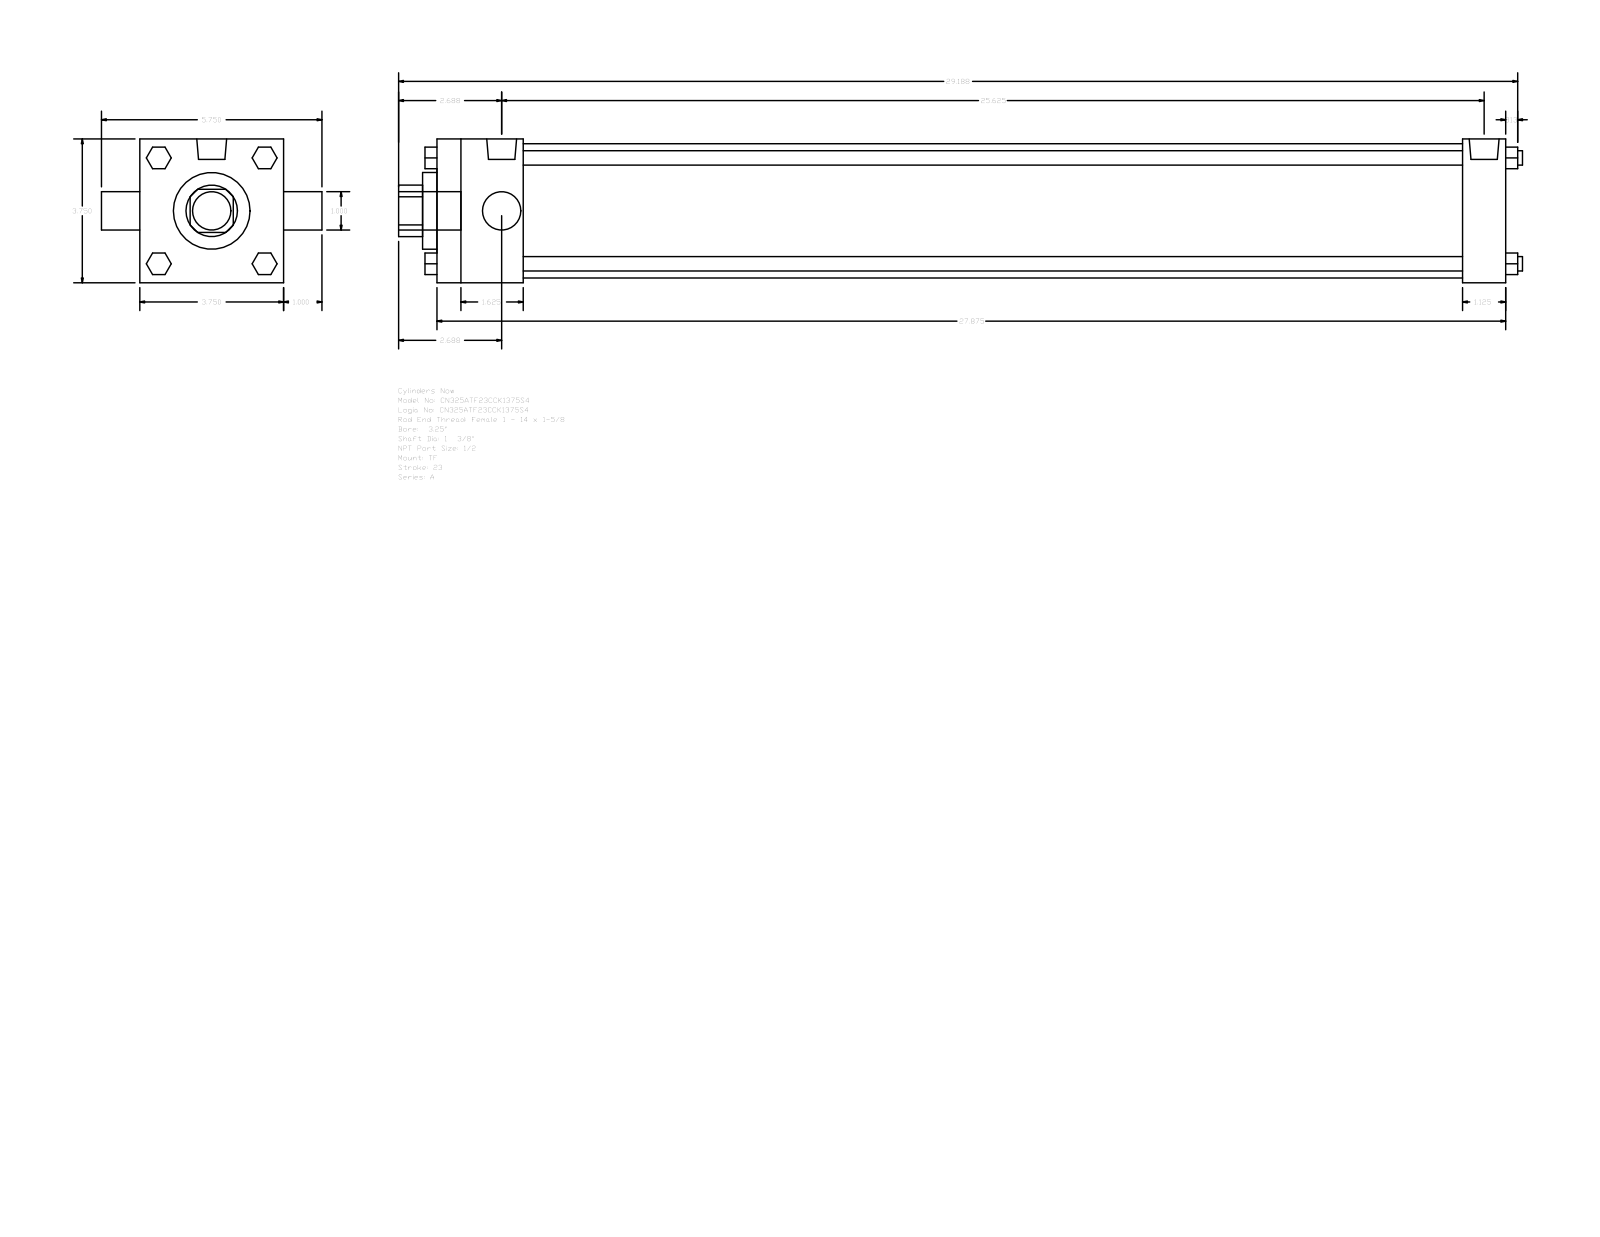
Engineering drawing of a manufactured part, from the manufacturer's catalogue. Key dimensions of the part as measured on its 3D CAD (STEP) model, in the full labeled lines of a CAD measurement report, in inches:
Part name (STEP PRODUCT): A_TF__0325_1.375
STEP written by: GSSL Pune (CONFIG_CONTROL_DESIGN)
Units: inches
Bodies: 0 solids, 120 faces (92 planar, 28 cylindrical, 0 other)
Overall size (bounding box): 29.313 × 5.75 × 3.75
Round holes (diameter × count): ⌀1 ×1, ⌀1.375 ×1, ⌀2 ×1, ⌀3.5 ×1
Round bosses / shafts (diameter × count): ⌀0.375 ×4, ⌀0.344 ×3, ⌀0.778 ×2, ⌀1 ×1
Partial cylindrical surfaces — rounded edges, fillets, slot ends (radius × count): R0.672 ×1
Main face-to-face distances: 3.75, 27.875, 1.125, 2.25, 26.75, 24.5, 25.625, 0.375, 2.625, 27.125
